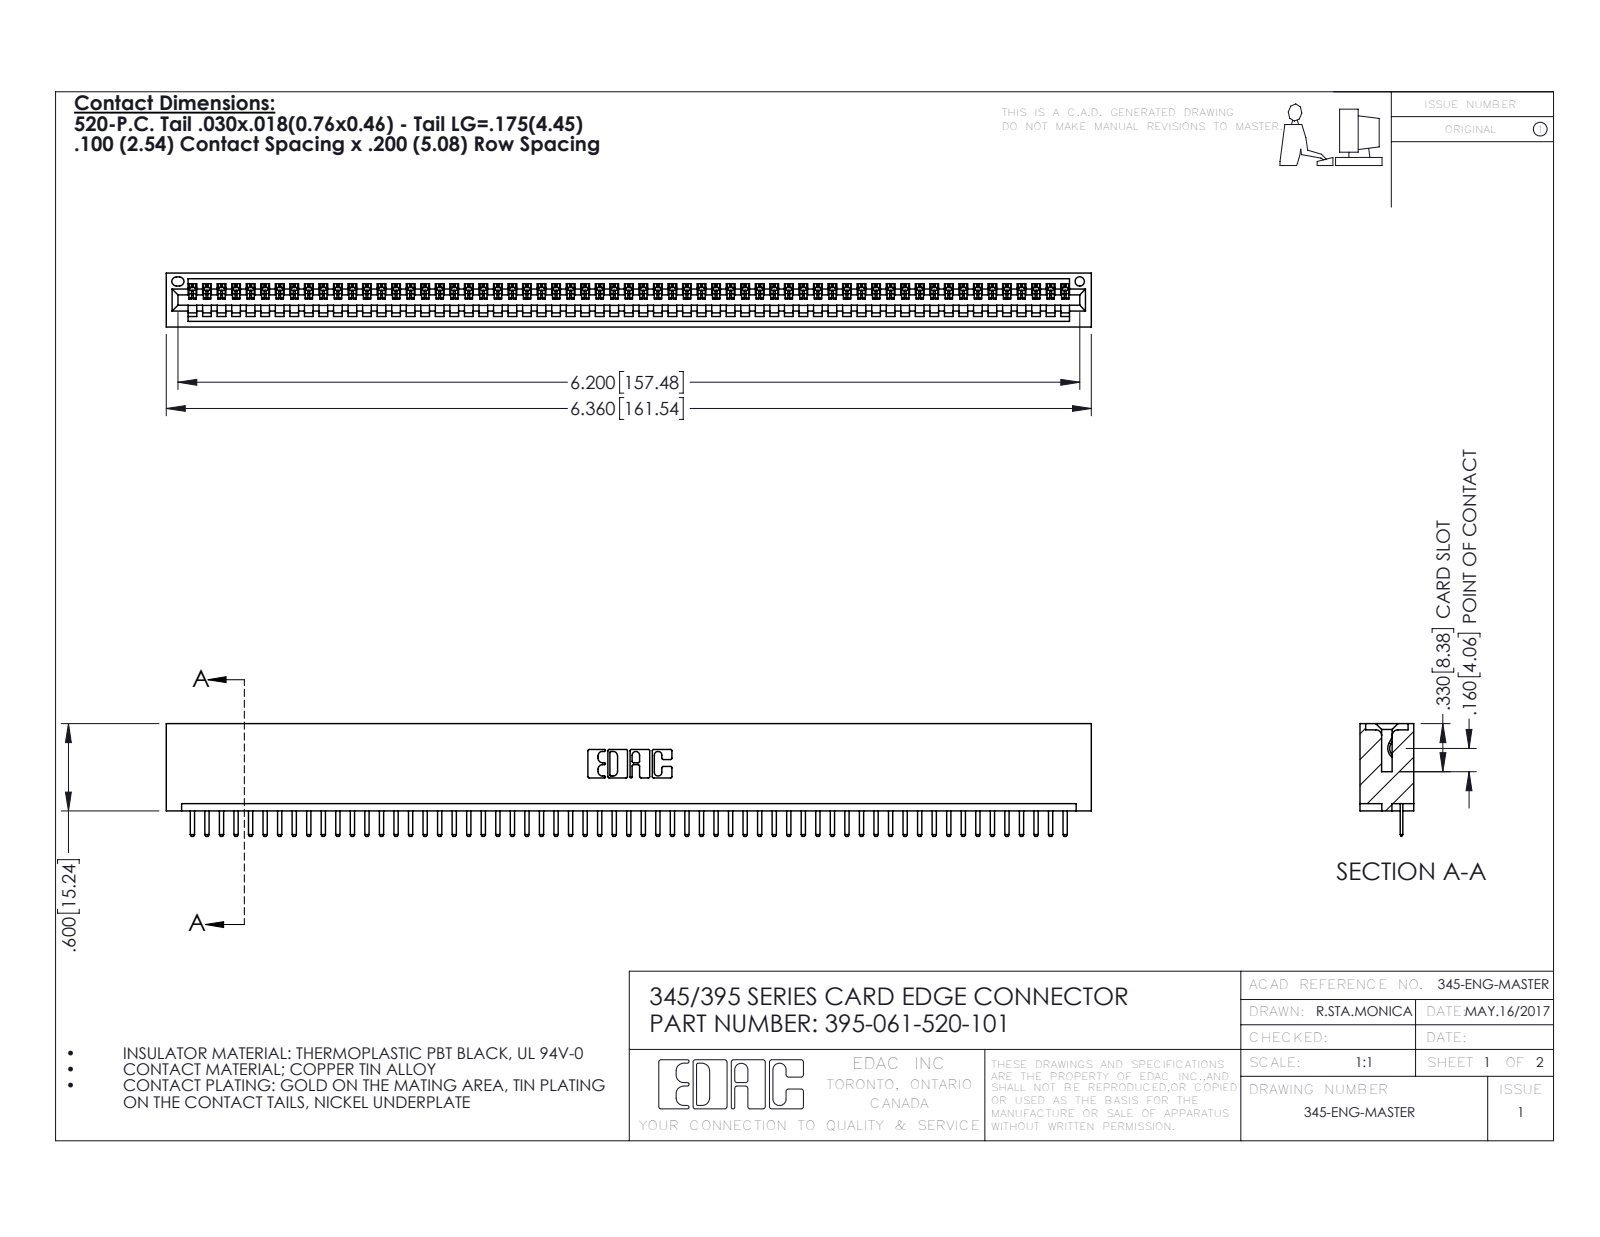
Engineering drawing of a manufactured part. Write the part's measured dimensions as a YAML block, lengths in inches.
part_name: "345 Part_No Mounting Lugs; 345-292-001_345-293-120; 395-061-520-101"
step_written_by: "SolidWorks 2016 (CONFIG_CONTROL_DESIGN)"
units: inches
bodies: {solids: 62, faces: 3900, planar: 2638, cylindrical: 1262, other: 0}
overall_size: [6.36, 0.775, 0.37]
volume: 0.971
surface_area: 32.57
round_holes:
  - {diameter: 0.064, count: 1}
partial_cylinders:
  - {radius: 0.01, count: 124}
  - {radius: 0.006, count: 122}
  - {radius: 0.01, count: 22}
  - {radius: 0.007, count: 6}
  - {radius: 0.031, count: 6}
  - {radius: 0.026, count: 3}
  - {radius: 0.031, count: 2}
  - {radius: 0.04, count: 2}
face_to_face_distances: [0.298, 0.072, 0.37, 0.2, 0.098, 0.272, 0.025, 0.225, 0.072, 0.149]
